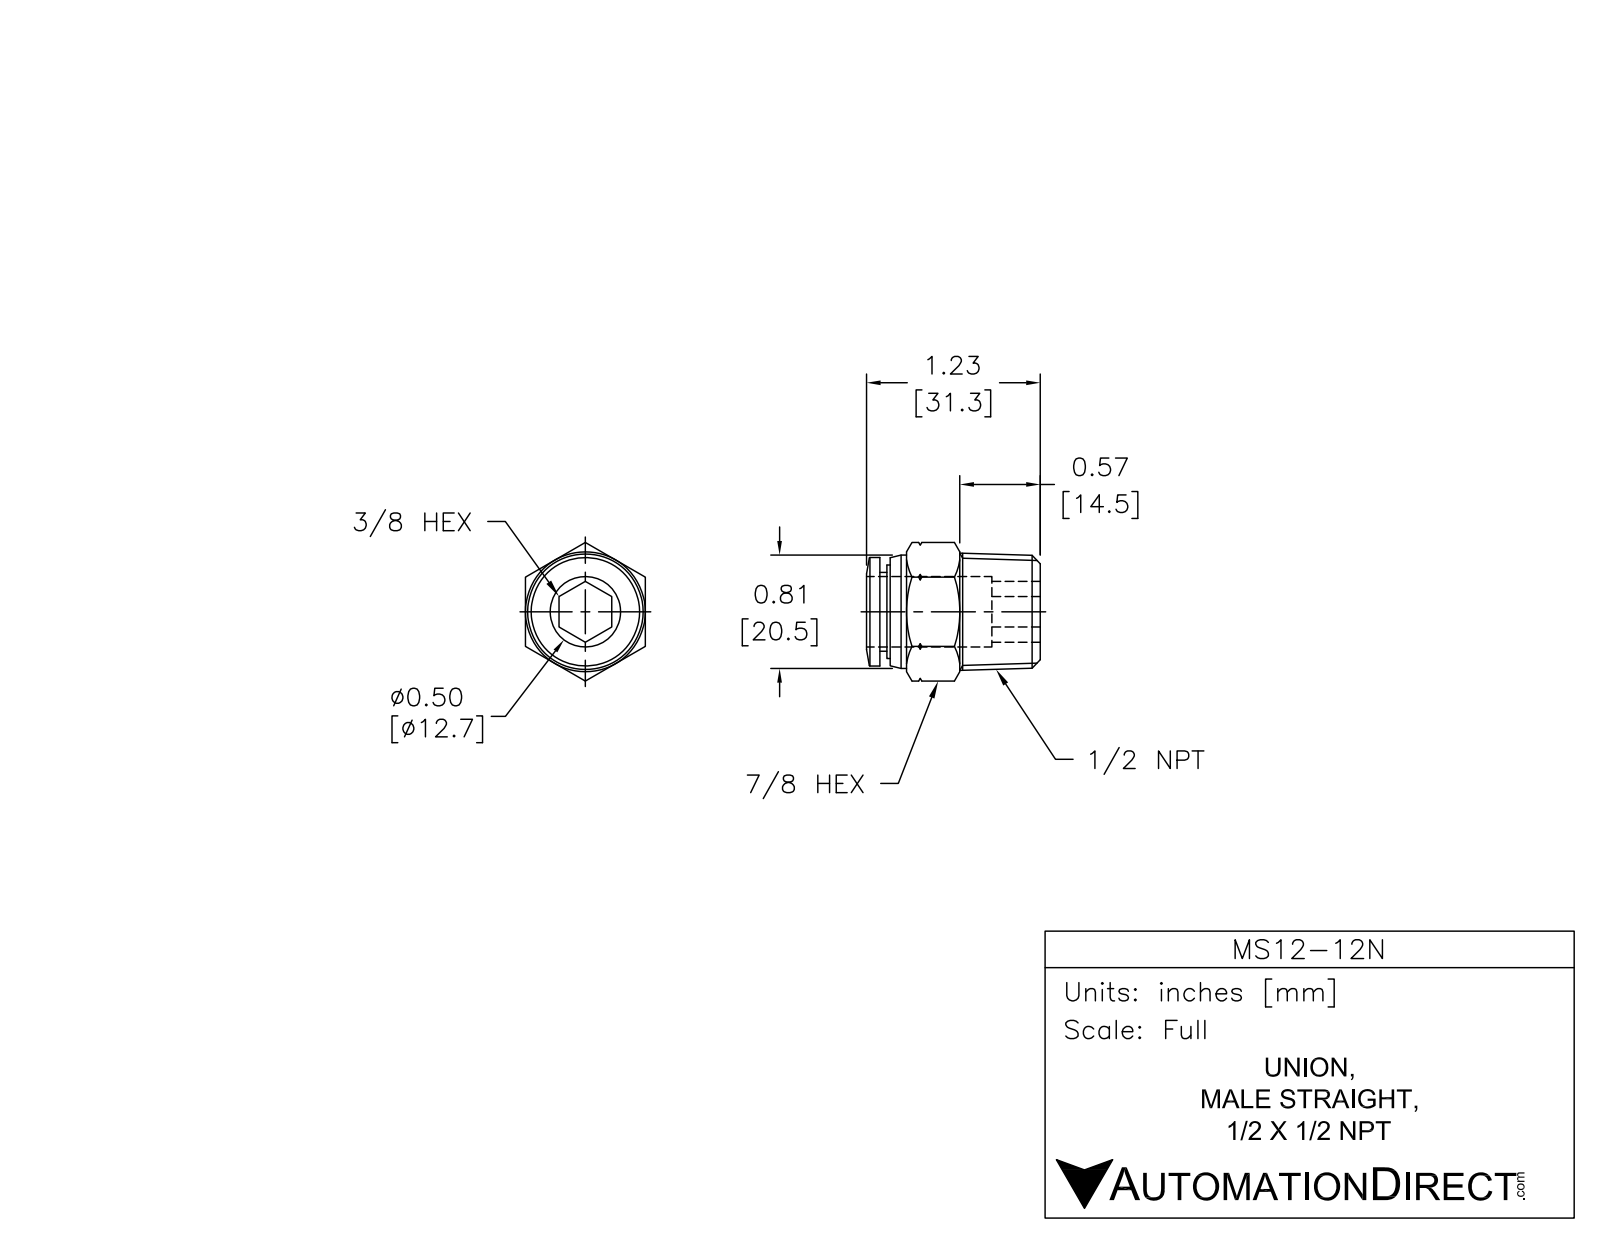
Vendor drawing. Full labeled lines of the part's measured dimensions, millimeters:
Part name (STEP PRODUCT): PC1-2--N04
STEP written by: Autodesk Inventor 2008 (AUTOMOTIVE_DESIGN)
Units: millimetres
Bodies: 1 solid, 50 faces (13 planar, 6 cylindrical, 31 other)
Overall size (bounding box): 31.35 × 25.4 × 22
Volume: 7 389 mm³ · Surface area: 4 097 mm²
Round holes (diameter × count): ⌀9.5 ×1, ⌀12.95 ×1
Round bosses / shafts (diameter × count): ⌀20.8 ×1, ⌀19.9 ×1, ⌀17.15 ×1, ⌀14.45 ×1
Main face-to-face distances: 22, 28.9, 27, 1.9, 27.6, 0.6, 1.3, 8.75, 18.25, 18.85
